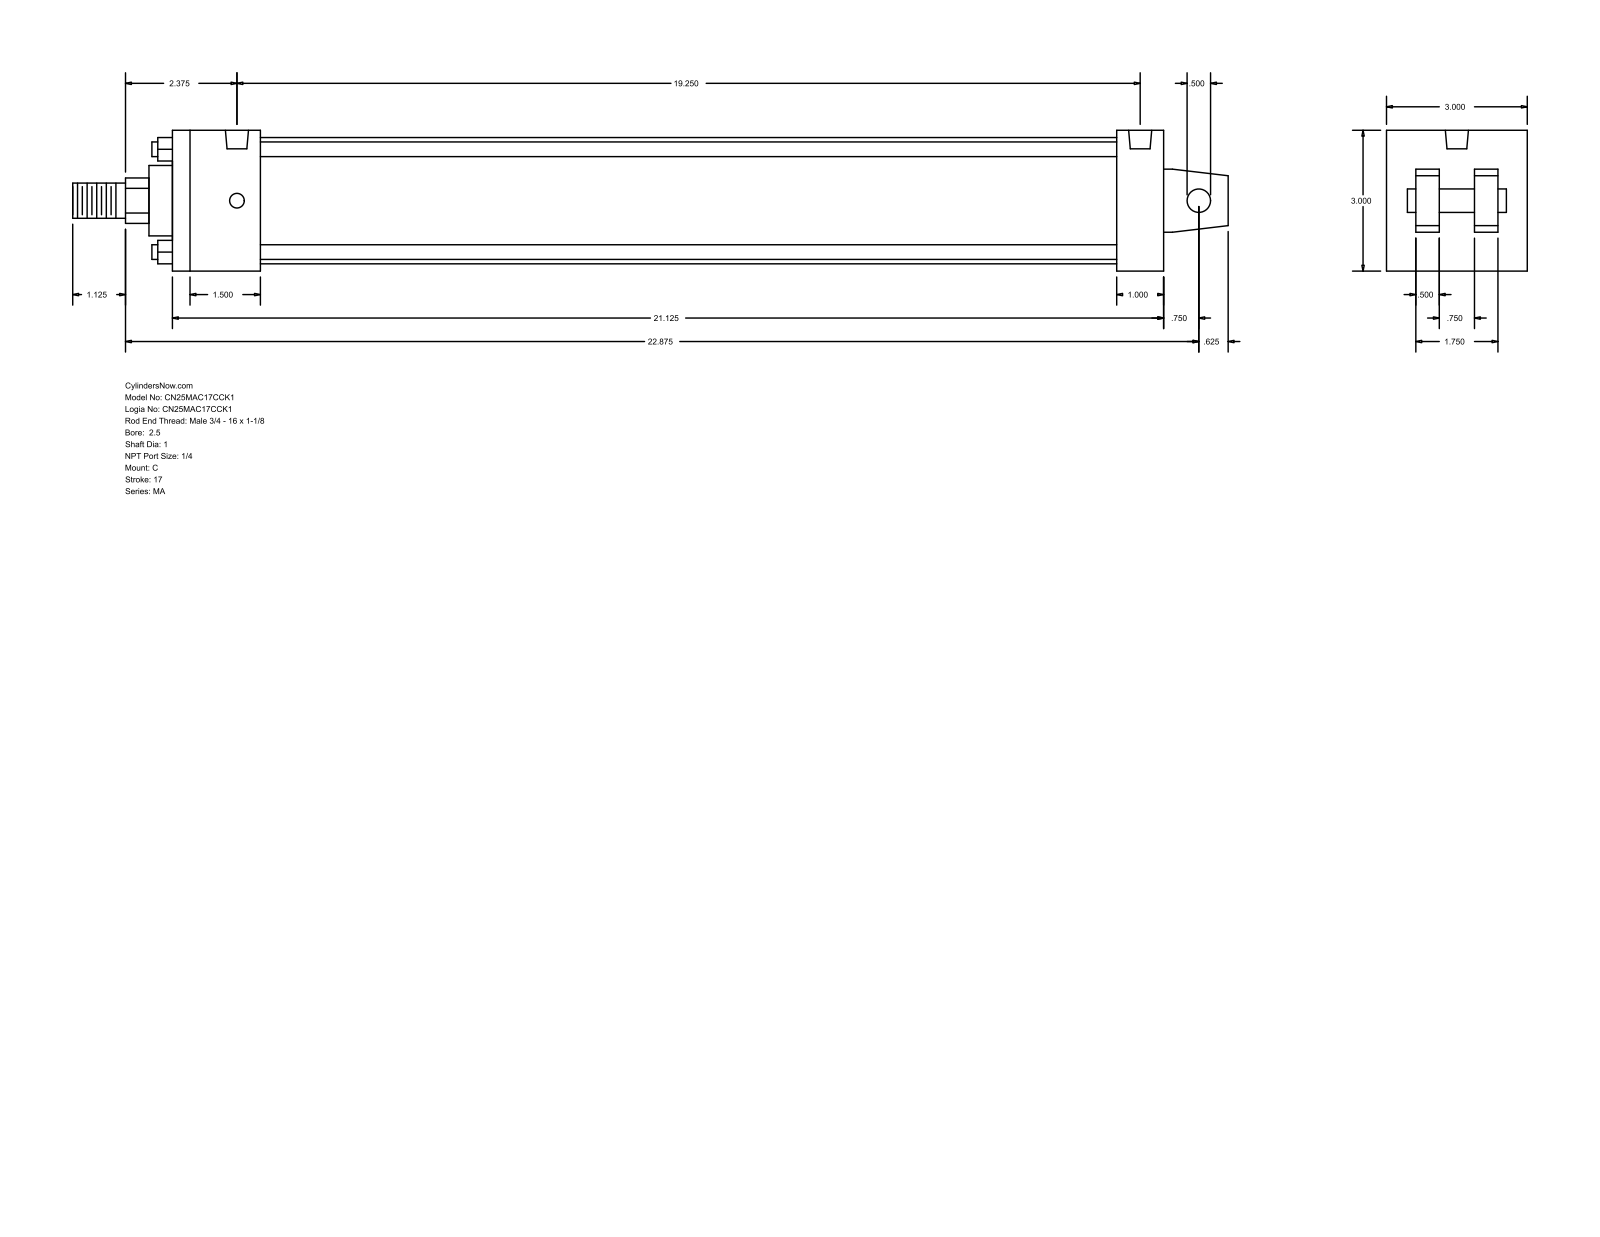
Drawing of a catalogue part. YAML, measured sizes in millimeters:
part_name: "MA_C__0250_1"
step_written_by: "GSSL Pune (CONFIG_CONTROL_DESIGN)"
units: millimeters
bodies: {solids: 0, faces: 103, planar: 76, cylindrical: 27, other: 0}
overall_size: [625.48, 76.2, 76.2]
round_holes:
  - {diameter: 7.94, count: 4}
  - {diameter: 12.49, count: 2}
round_bosses_or_shafts:
  - {diameter: 7.94, count: 4}
  - {diameter: 68.33, count: 1}
  - {diameter: 38.1, count: 1}
  - {diameter: 25.4, count: 1}
  - {diameter: 19.05, count: 1}
  - {diameter: 12.7, count: 1}
partial_cylinders:
  - {radius: 12.29, count: 1}
face_to_face_distances: [76.2, 536.58, 47.63, 12.7, 60.33, 15.87, 25.4, 28.57, 511.18, 463.55]
hole_center_spacings: [488.94]
